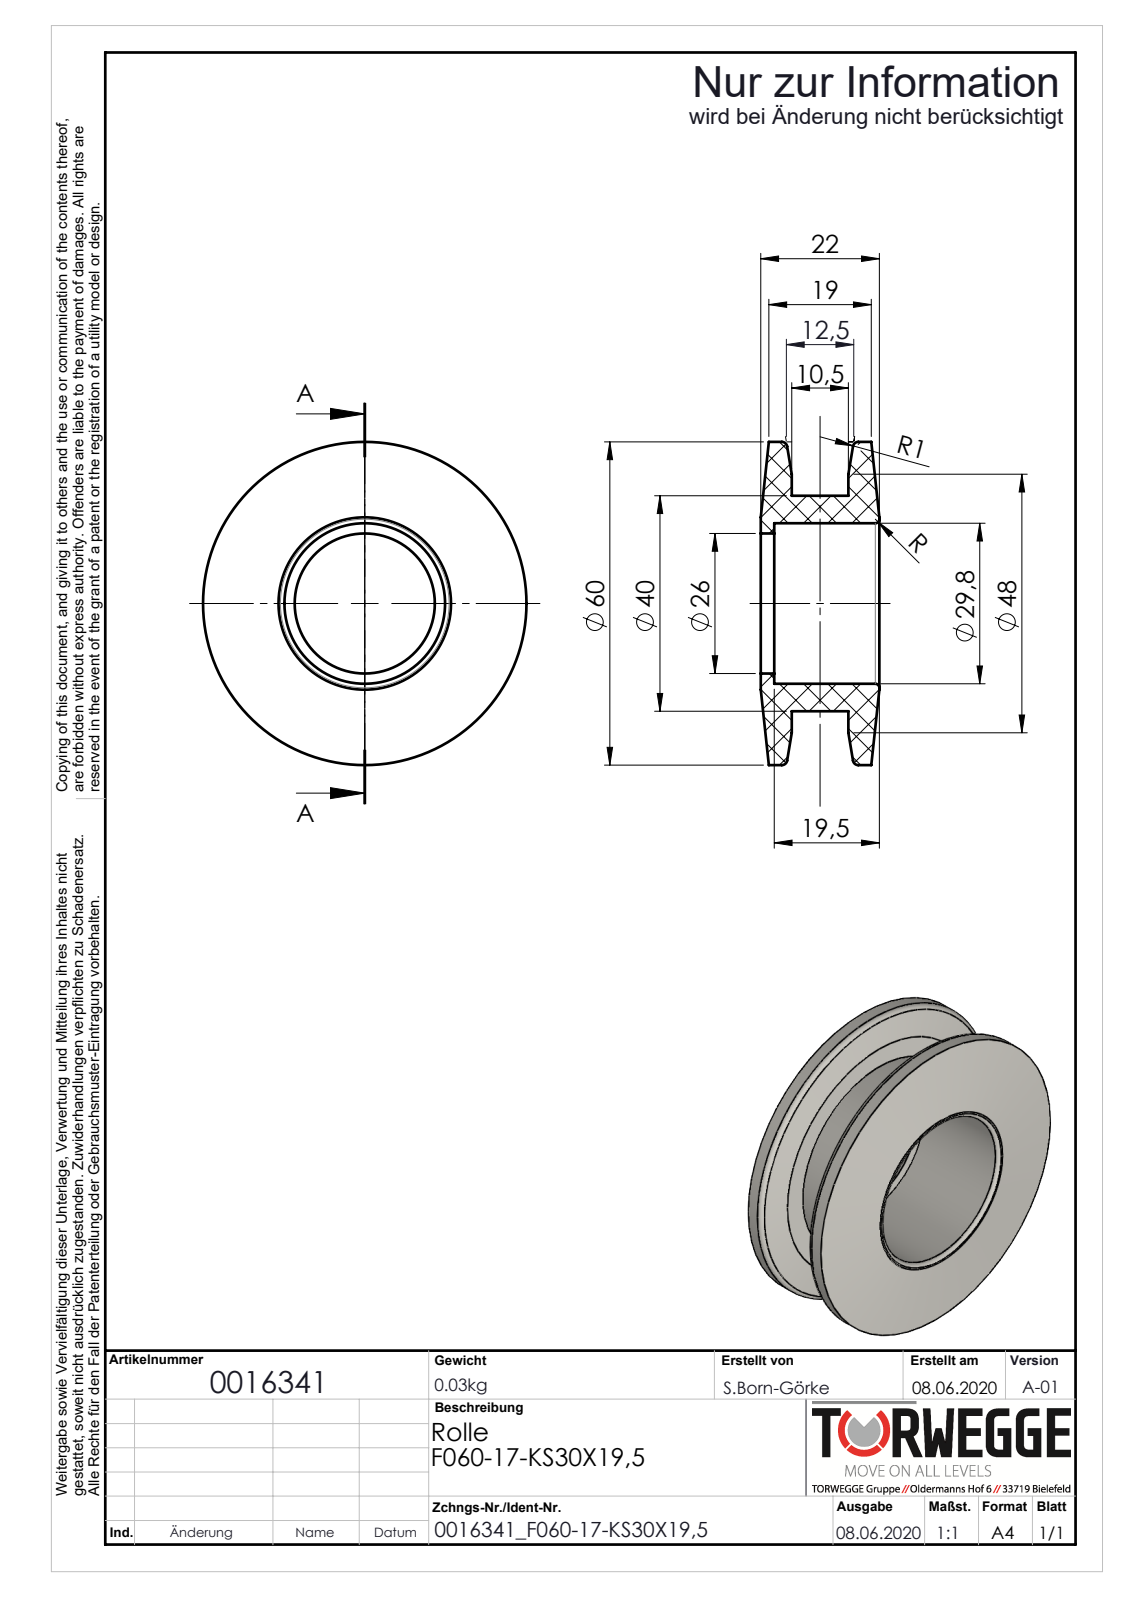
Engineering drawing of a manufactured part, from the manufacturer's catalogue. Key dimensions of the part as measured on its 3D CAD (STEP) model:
Part name (STEP PRODUCT): 0016341
STEP written by: SolidWorks 2018 (AUTOMOTIVE_DESIGN)
Units: millimetres
Bodies: 1 solid, 29 faces (5 planar, 10 cylindrical, 14 other)
Overall size (bounding box): 60 × 60 × 22
Volume: 26 319 mm³ · Surface area: 12 221 mm²
Round holes (diameter × count): ⌀26 ×1, ⌀29.8 ×1
Round bosses / shafts (diameter × count): ⌀60 ×1, ⌀40 ×1
Main face-to-face distances: 10.5, 5.75, 16.25, 13.75, 3.25, 2.5, 19.5, 22
